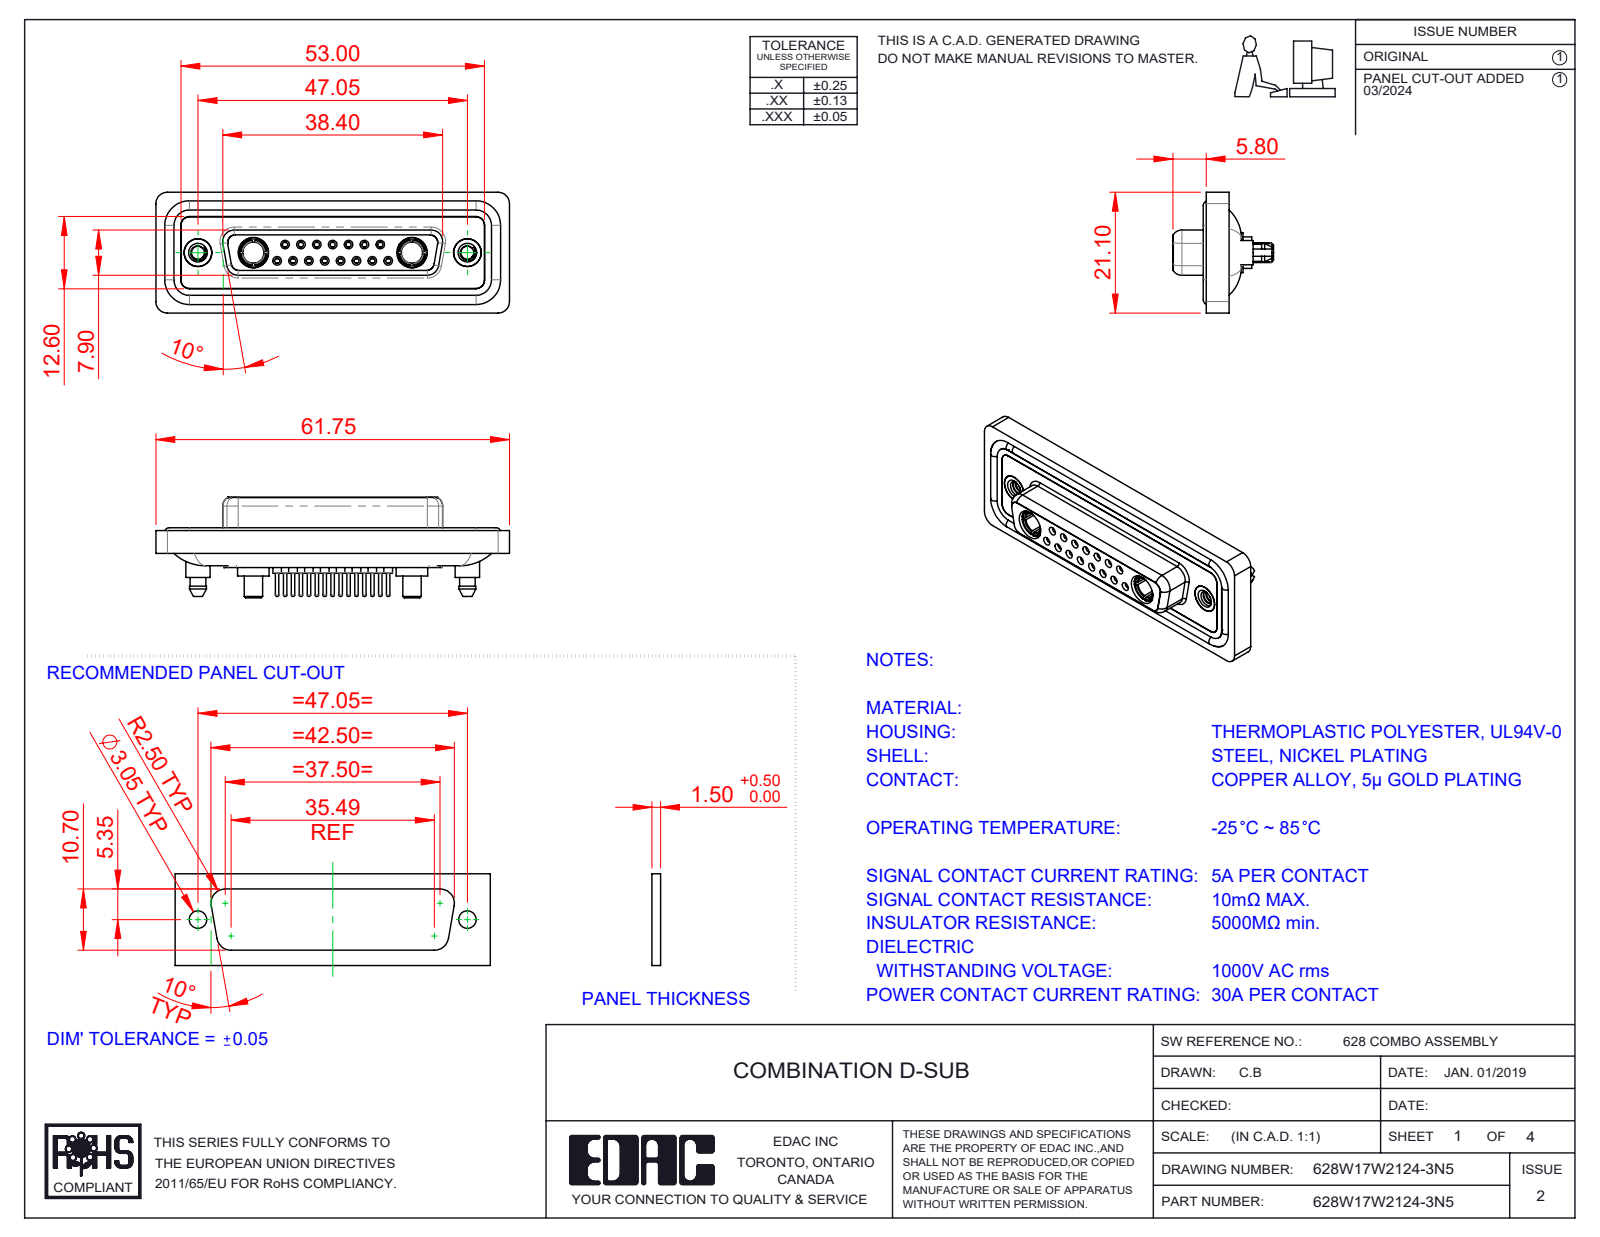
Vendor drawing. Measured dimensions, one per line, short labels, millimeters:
name: 628Combo Shell Rear_25 Contacts; 628Combo Contact Row 2_24; 628Combo Shell Front_25 Contacts; 628W17W2124-3N5 (+5 more)
written by: SolidWorks 2023 (CONFIG_CONTROL_DESIGN)
unit: mm
bodies: 26 solids, 1409 faces (404 planar, 551 cylindrical, 454 other)
size: 61.75 × 21.1 × 17.55
volume: 8 472 mm³; area: 14 197 mm²
holes: 15× ⌀0.9, 15× ⌀1.1, 15× ⌀1.5, 15× ⌀2, 8× ⌀1.6, 7× ⌀1.7, 4× ⌀4.85, 2× ⌀2.26, 2× ⌀3.7, 2× ⌀4, 2× ⌀4.05, 2× ⌀5
bosses: 15× ⌀2.2, 15× ⌀0.6, 11× ⌀1.6, 2× ⌀5.5, 2× ⌀5.4, 2× ⌀5.2, 2× ⌀4.96, 2× ⌀4.95
rounds: 24× R1.5, 18× R2, 10× R1.6, 8× R1.35, 4× R0.25, 4× R0.5, 4× R0.6, 4× R0.65
face distances: 0.4, 1.8, 7.45, 5.65, 6.6, 0.5, 7.05, 1.6, 2.9, 1.1
hole spacings: 3.16, 2.77, 8.31, 5.54, 5.03, 5.04, 7.49, 11.08
